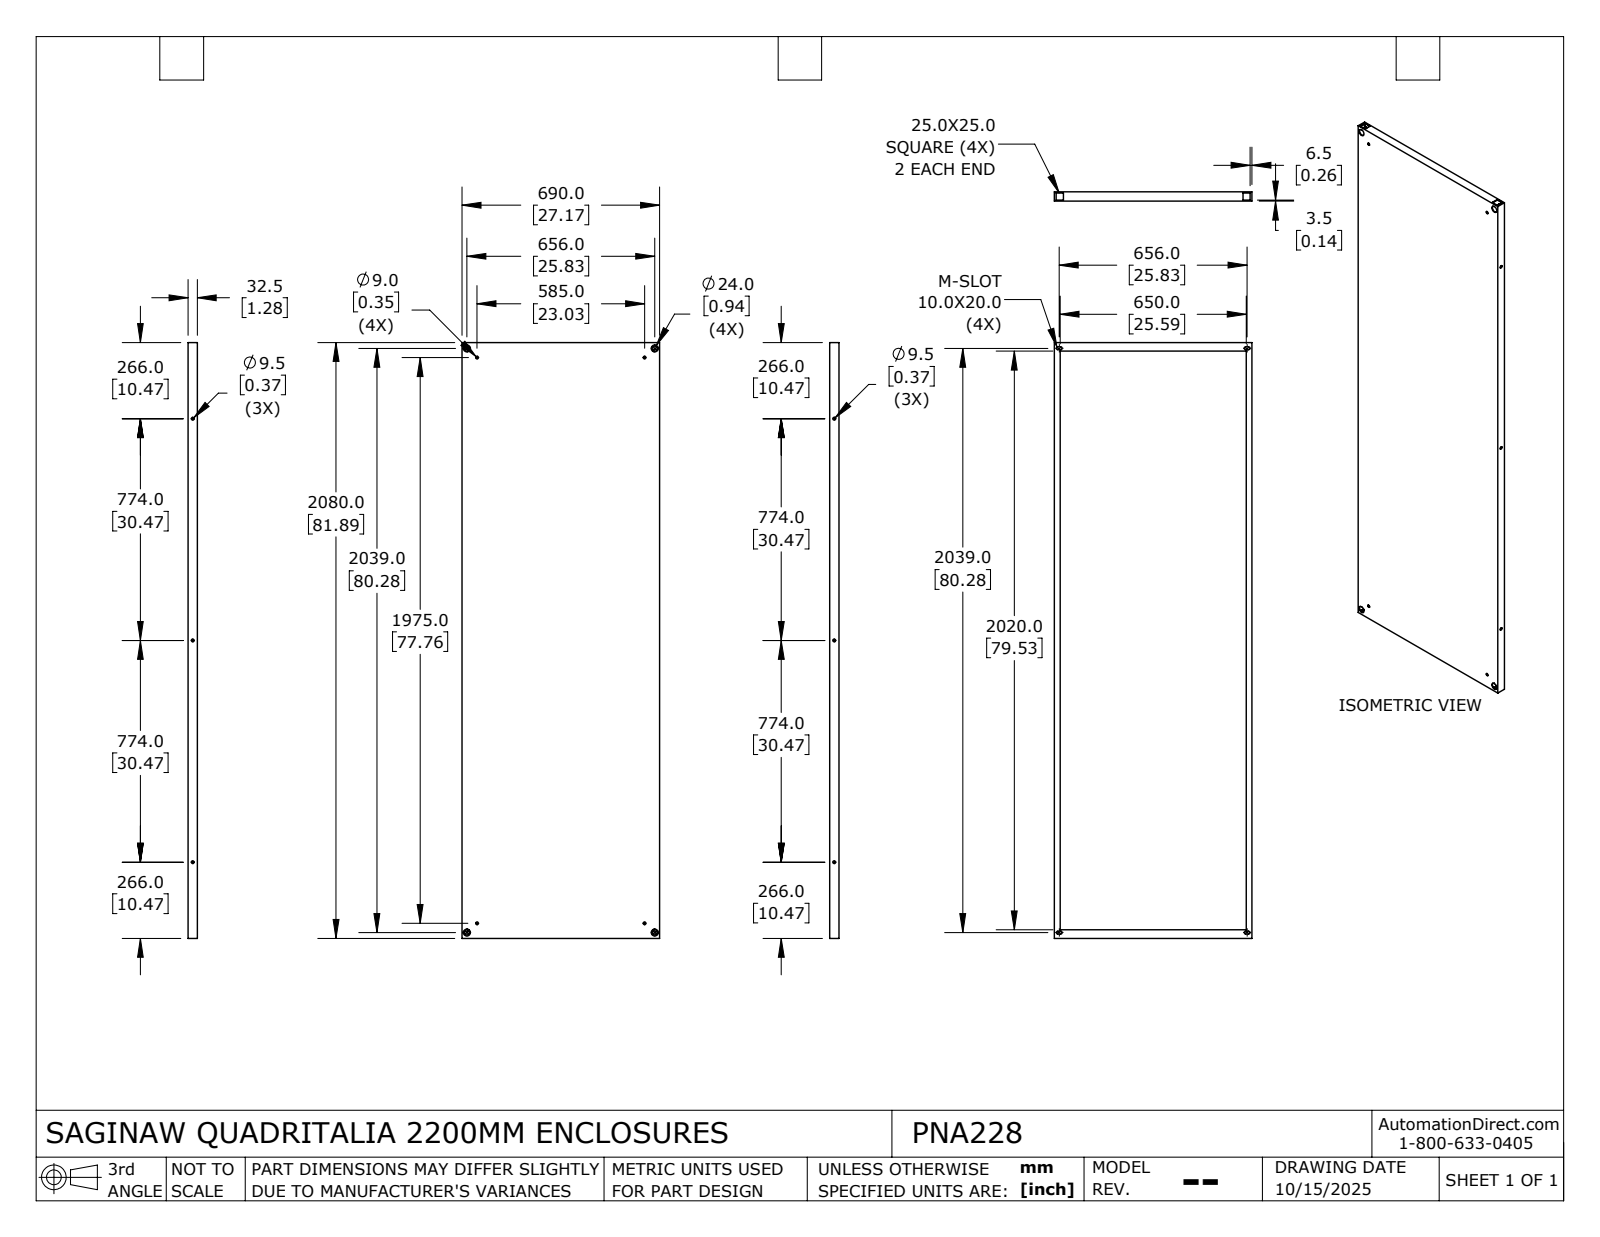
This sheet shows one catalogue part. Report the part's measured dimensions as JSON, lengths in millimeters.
{"part_name": "PNA228", "step_written_by": "SolidWorks 2024 (AUTOMOTIVE_DESIGN)", "units": "millimeters", "bodies": {"solids": 1, "faces": 94, "planar": 64, "cylindrical": 30, "other": 0}, "overall_size": [2080, 690, 32.5], "volume_mm3": 4259000, "surface_area_mm2": 3424000, "round_holes": [[9, 4], [24, 4], [9.5, 3]], "partial_cylinders_radius": [[5, 8]], "face_to_face_distances": [2.5, 30, 32.5, 687.5, 27.5, 690, 685, 2077.5, 2080, 2075], "hole_center_spacings": [47.79, 621.32, 2007.31, 2100.73, 585, 656, 774, 1975]}
